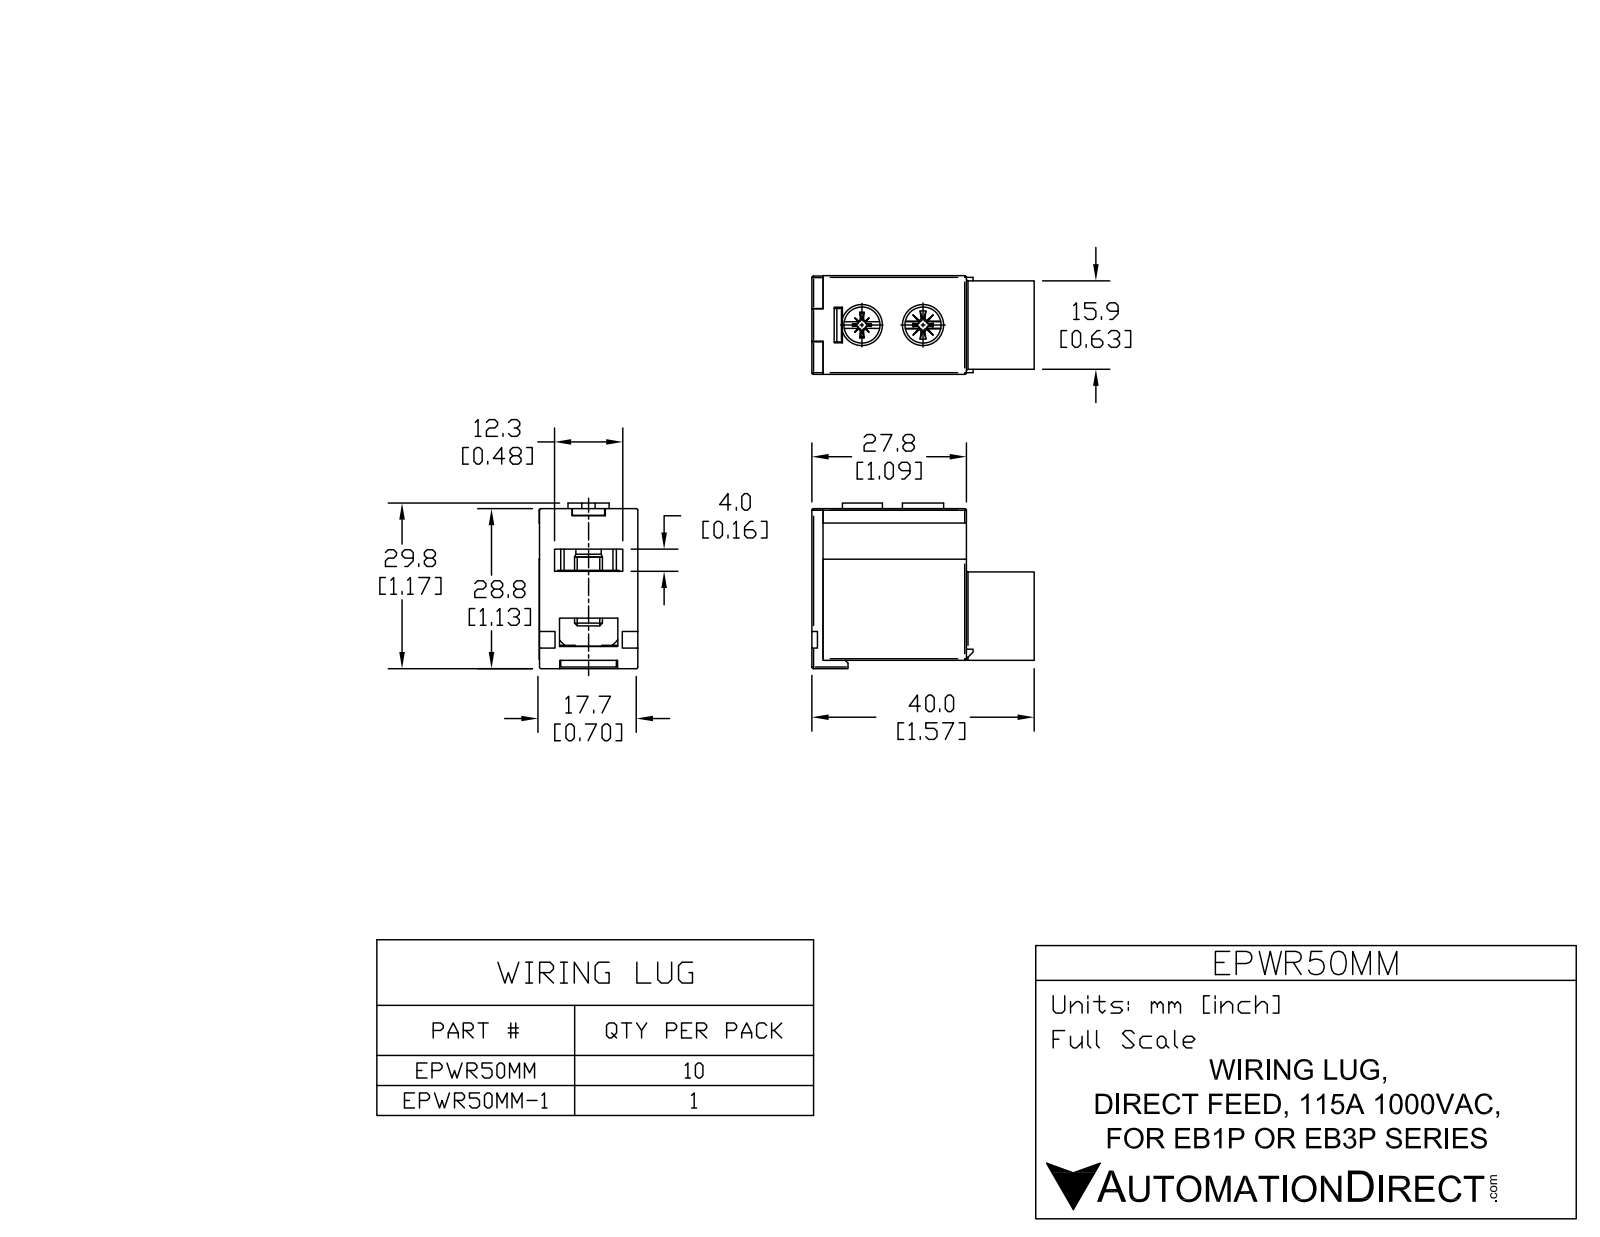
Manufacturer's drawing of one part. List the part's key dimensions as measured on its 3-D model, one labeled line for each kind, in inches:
Part name (STEP PRODUCT): EPWR50MM
STEP written by: SolidWorks 2011 (AUTOMOTIVE_DESIGN)
Units: inches
Bodies: 1 solid, 145 faces (121 planar, 20 cylindrical, 4 other)
Overall size (bounding box): 1.575 × 1.18 × 0.758
Volume: 0.645 in³ · Surface area: 10.45 in²
Round holes (diameter × count): ⌀0.255 ×2, ⌀0.525 ×1
Round bosses / shafts (diameter × count): ⌀0.3 ×2, ⌀0.625 ×1
Partial cylindrical surfaces — rounded edges, fillets, slot ends (radius × count): R0.015 ×2
Main face-to-face distances: 0.698, 1.075, 0.06, 0.638, 1.1, 0.06, 0.1, 0.698, 0.758, 1
Hole centre spacings: 0.45
